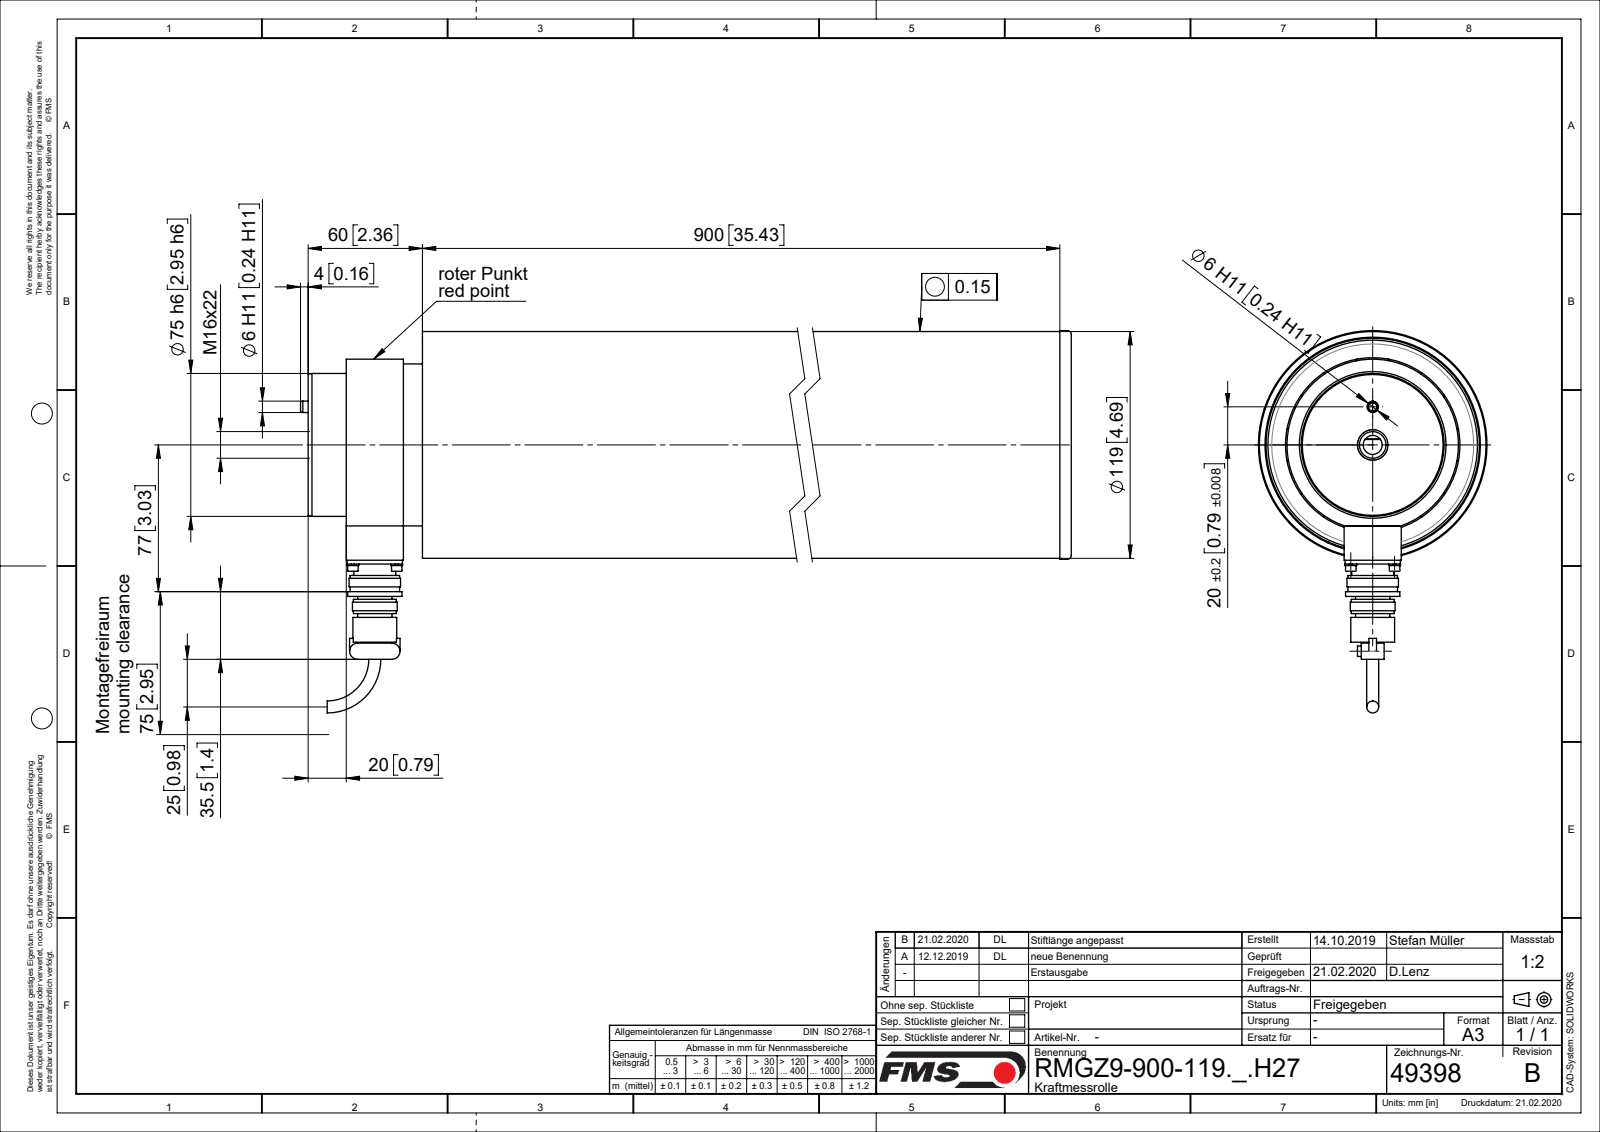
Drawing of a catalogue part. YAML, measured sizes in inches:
part_name: "Spannstift_ISO13337_D06x12; Lamellenstopfen_D_120; Federringe_DIN127A_M03; 49398_stp (+8 more)"
step_written_by: "SolidWorks 2018 (CONFIG_CONTROL_DESIGN)"
units: inches
bodies: {solids: 37, faces: 544, planar: 154, cylindrical: 214, other: 176}
overall_size: [38.189, 7.9, 4.724]
volume: 201.9
surface_area: 1564
round_holes:
  - {diameter: 0.098, count: 4}
  - {diameter: 0.122, count: 4}
  - {diameter: 0.134, count: 4}
  - {diameter: 0.197, count: 1}
  - {diameter: 0.236, count: 1}
  - {diameter: 0.394, count: 1}
  - {diameter: 0.472, count: 1}
  - {diameter: 0.551, count: 1}
  - {diameter: 0.866, count: 1}
  - {diameter: 0.906, count: 1}
  - {diameter: 1.024, count: 1}
  - {diameter: 1.575, count: 1}
round_bosses_or_shafts:
  - {diameter: 0.217, count: 6}
  - {diameter: 0.244, count: 4}
  - {diameter: 0.118, count: 4}
  - {diameter: 0.098, count: 4}
  - {diameter: 4.724, count: 1}
  - {diameter: 4.685, count: 1}
  - {diameter: 4.173, count: 1}
  - {diameter: 3.543, count: 1}
partial_cylinders:
  - {radius: 0.433, count: 4}
  - {radius: 0.167, count: 2}
  - {radius: 1.083, count: 1}
face_to_face_distances: [1.969, 0.079, 1.063, 5.866, 0.236, 27.992, 0.787, 0.394, 28.071, 1.378]
hole_center_spacings: [0.64, 0.906, 1.281, 0.787]
